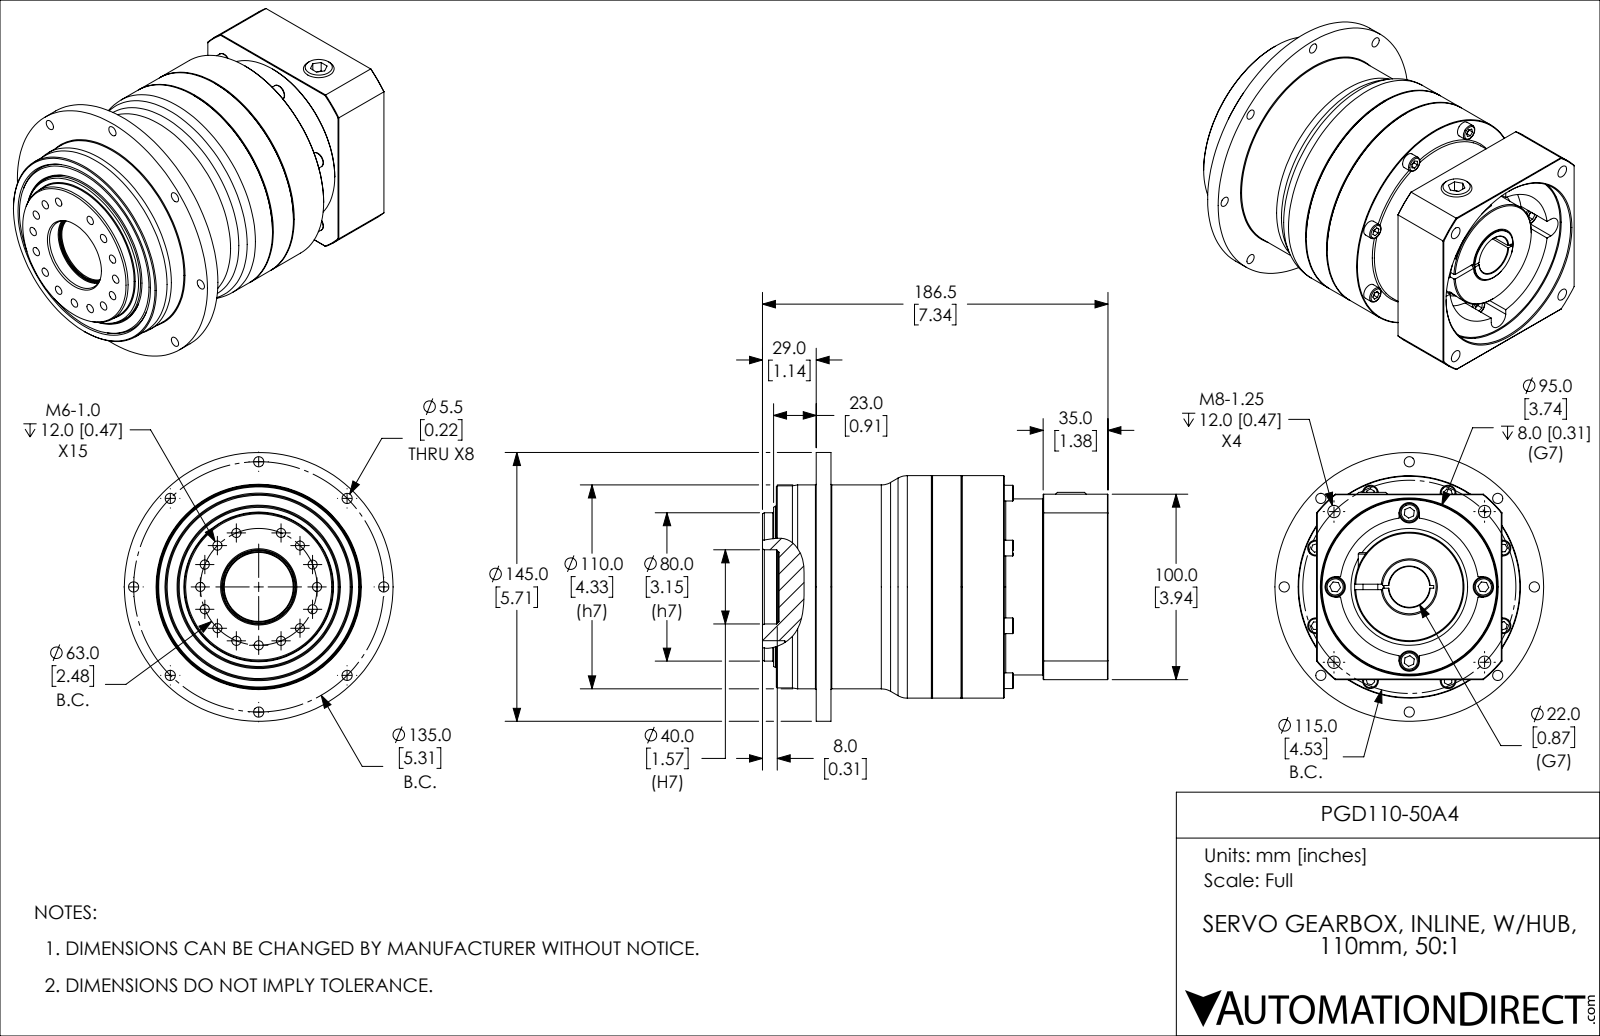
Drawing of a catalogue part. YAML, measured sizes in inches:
part_name: "PGD110-50A4"
step_written_by: "SolidWorks 2015 (AUTOMOTIVE_DESIGN)"
units: inches
bodies: {solids: 12, faces: 497, planar: 240, cylindrical: 180, other: 77}
overall_size: [7.343, 5.709, 5.709]
volume: 103.9
surface_area: 231.6
round_holes:
  - {diameter: 0.194, count: 11}
  - {diameter: 0.217, count: 8}
  - {diameter: 0.194, count: 4}
  - {diameter: 0.262, count: 3}
  - {diameter: 0.262, count: 1}
  - {diameter: 0.346, count: 1}
  - {diameter: 0.512, count: 1}
  - {diameter: 0.591, count: 1}
  - {diameter: 0.866, count: 1}
  - {diameter: 1.465, count: 1}
  - {diameter: 1.543, count: 1}
  - {diameter: 2.402, count: 1}
round_bosses_or_shafts:
  - {diameter: 0.335, count: 8}
  - {diameter: 0.394, count: 4}
  - {diameter: 0.315, count: 2}
  - {diameter: 5.709, count: 1}
  - {diameter: 4.724, count: 1}
  - {diameter: 4.331, count: 1}
  - {diameter: 3.15, count: 1}
  - {diameter: 2.146, count: 1}
partial_cylinders:
  - {radius: 0.217, count: 4}
  - {radius: 0.276, count: 1}
  - {radius: 2.52, count: 1}
face_to_face_distances: [0.157, 0.866, 1.024, 0.276, 5.965, 3.937, 5.728, 5.531, 0.787, 5.886]
hole_center_spacings: [1.585, 2.465, 3.335, 3.833, 0.484, 2.062, 2.933, 1.754]
